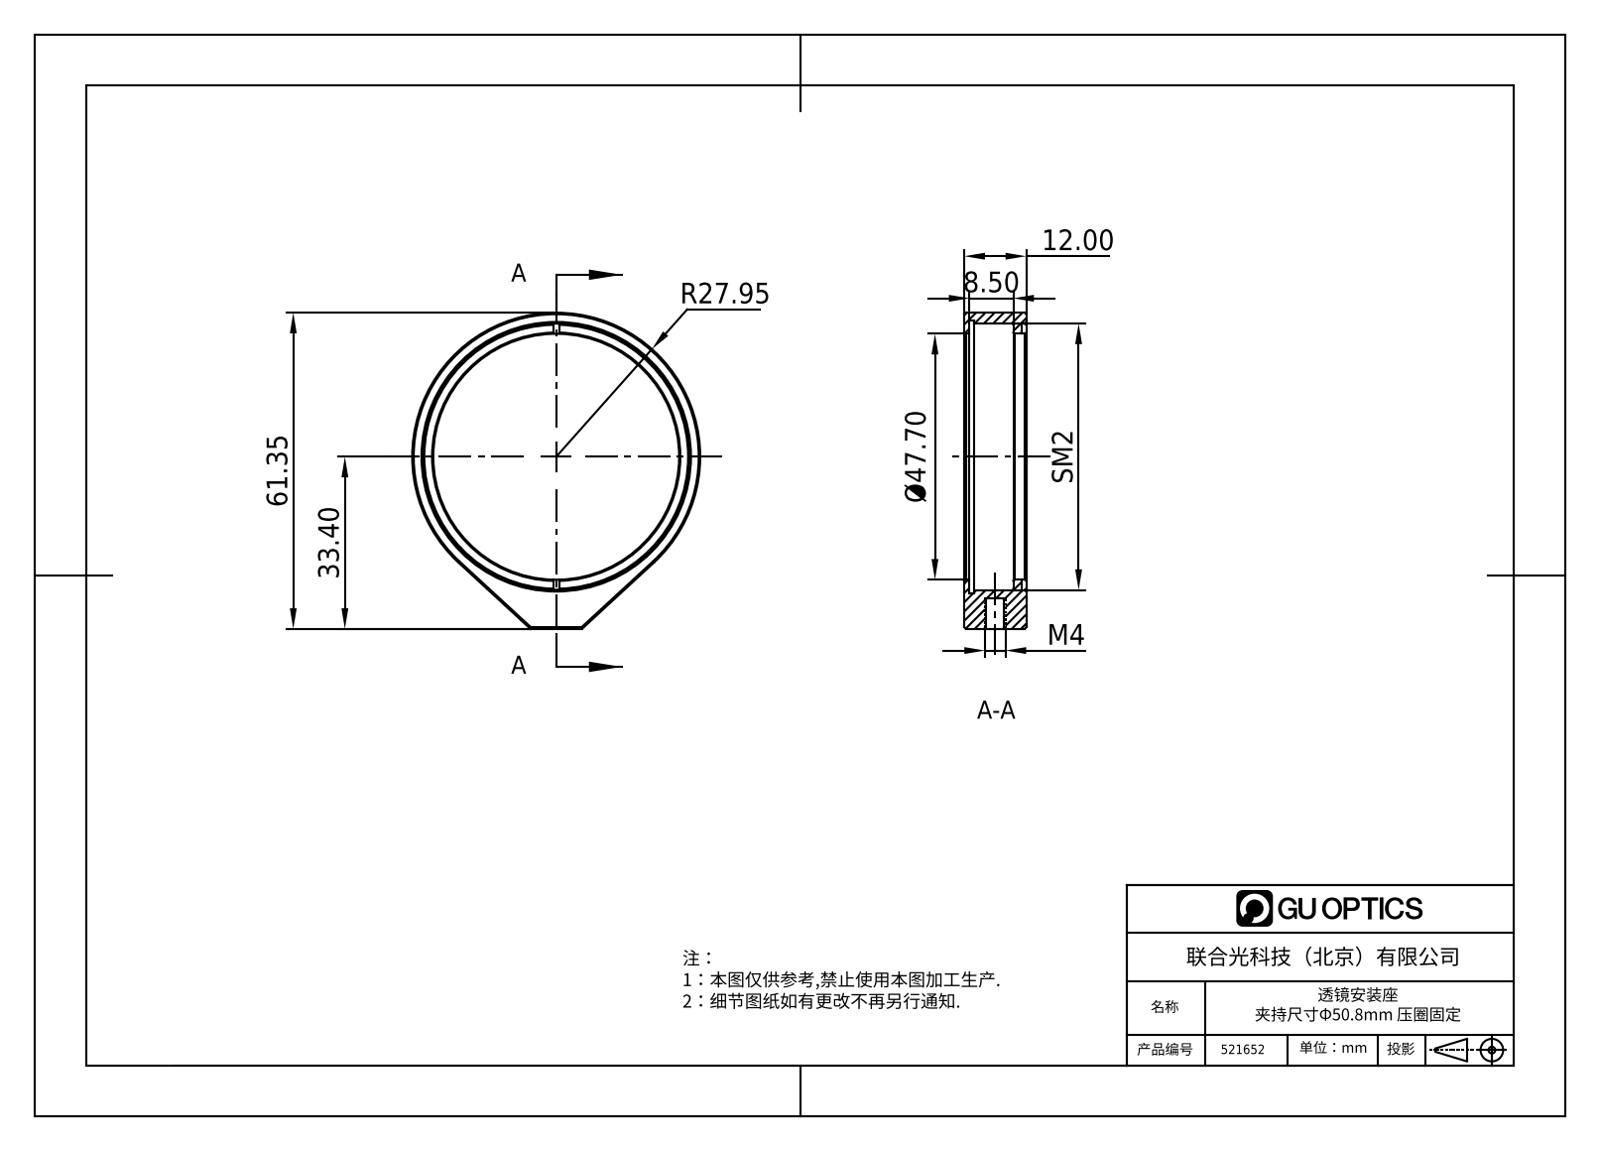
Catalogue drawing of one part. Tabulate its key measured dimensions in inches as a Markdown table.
| quantity | value |
| --- | --- |
| part name | 1.3.1.3-ZZT-2.0 |
| STEP written by | SolidWorks 2021 (CONFIG_CONTROL_DESIGN) |
| units | inches |
| bodies | 0 solids, 58 faces (21 planar, 15 cylindrical, 22 other) |
| overall size | 2.415 × 2.201 × 0.472 |
| round holes (diameter × count) | 0.157 × 1, 1.878 × 1, 1.878 × 1, 2.035 × 1, 2.083 × 1 |
| round bosses / shafts (diameter × count) | 2.035 × 1 |
| partial cylindrical surfaces (radius × count) | 1.1 × 1 |
| main face-to-face distances | 0.472, 0.039, 0.433, 0.374, 0.335, 0.098, 0.437, 0.398, 0.063, 0.035 |
